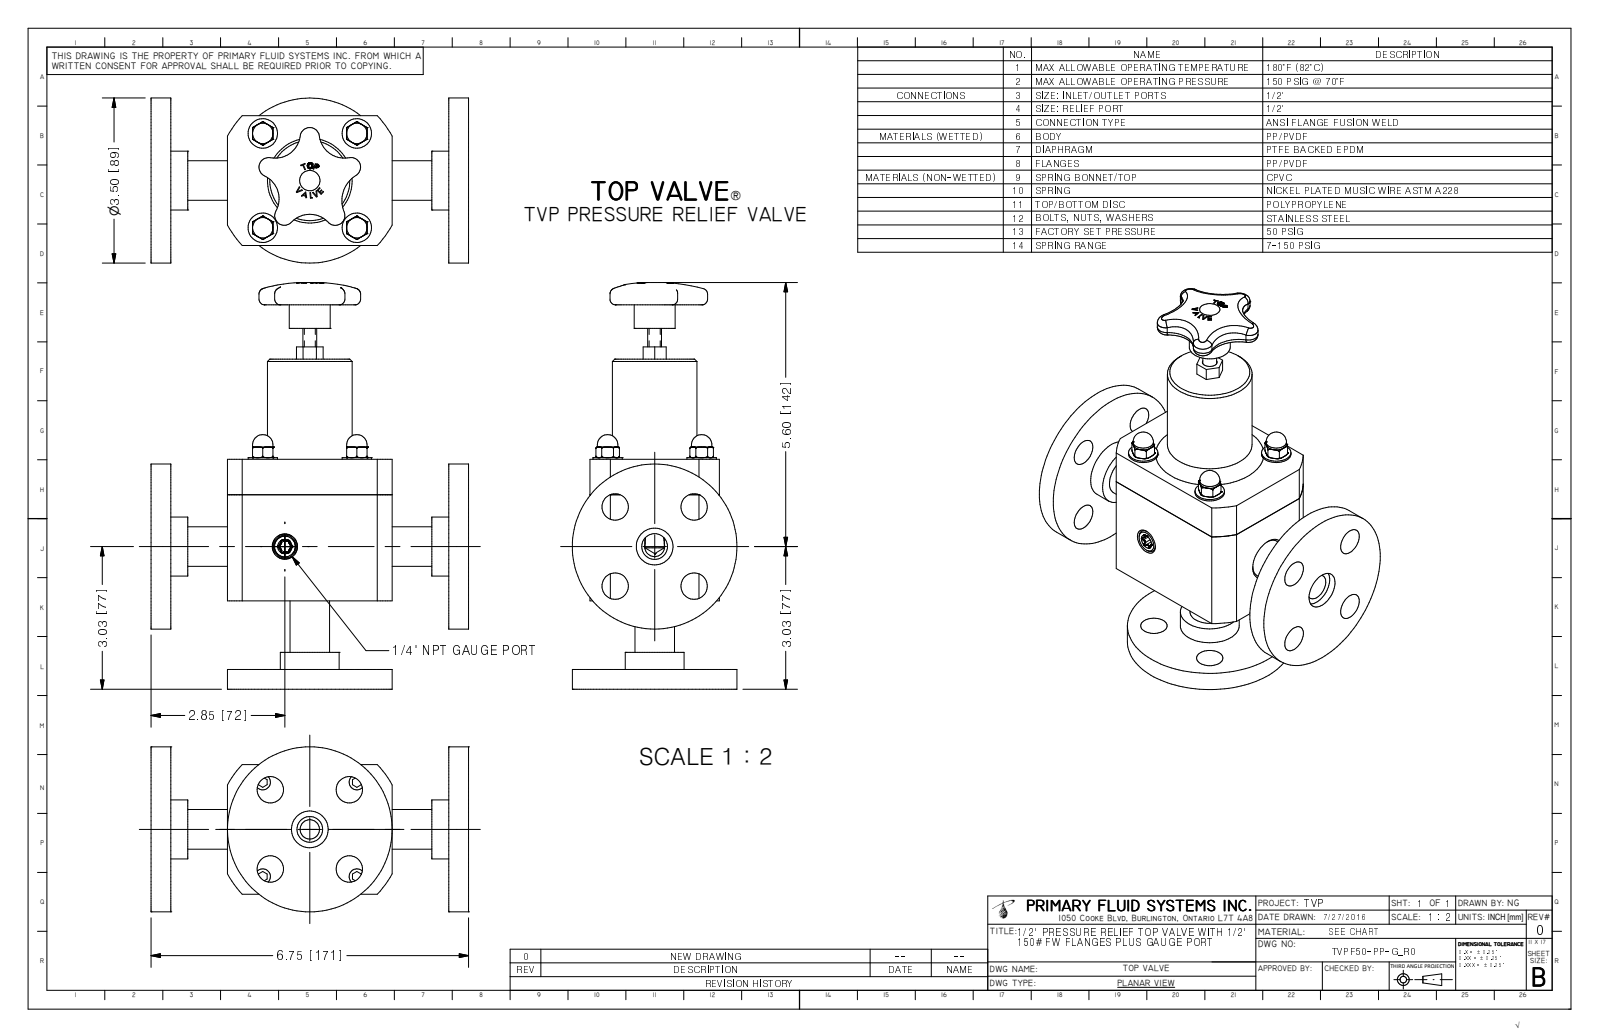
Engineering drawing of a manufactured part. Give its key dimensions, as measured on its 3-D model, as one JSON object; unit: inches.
{"part_name": "TVPF50-PP-G_R0", "step_written_by": "Autodesk Inventor 2009 (AUTOMOTIVE_DESIGN)", "units": "inches", "bodies": {"solids": 1, "faces": 361, "planar": 143, "cylindrical": 74, "other": 144}, "overall_size": [8.625, 6.75, 3.5], "volume_in3": 47.39, "surface_area_in2": 173.6, "round_holes": [[0.56, 8], [0.175, 4], [0.546, 2], [0.78, 2], [2.4, 1]], "round_bosses_or_shafts": [[0.625, 4], [0.433, 4], [3.5, 2], [1.25, 2], [0.84, 2], [2.375, 1], [1.8, 1], [0.87, 1]], "partial_cylinders_radius": [[0.027, 6], [0.085, 5], [0.205, 5], [0.536, 4], [0.656, 4], [0.625, 1], [0.745, 1], [1.988, 1]], "face_to_face_distances": [0.42, 6.33, 5.125, 1.625, 1.205, 4.705, 2.75, 1.875, 6.75, 1.455], "hole_center_spacings": [1.188, 1.68, 1.847, 0.227, 1.414, 2, 2.375, 2.602]}
